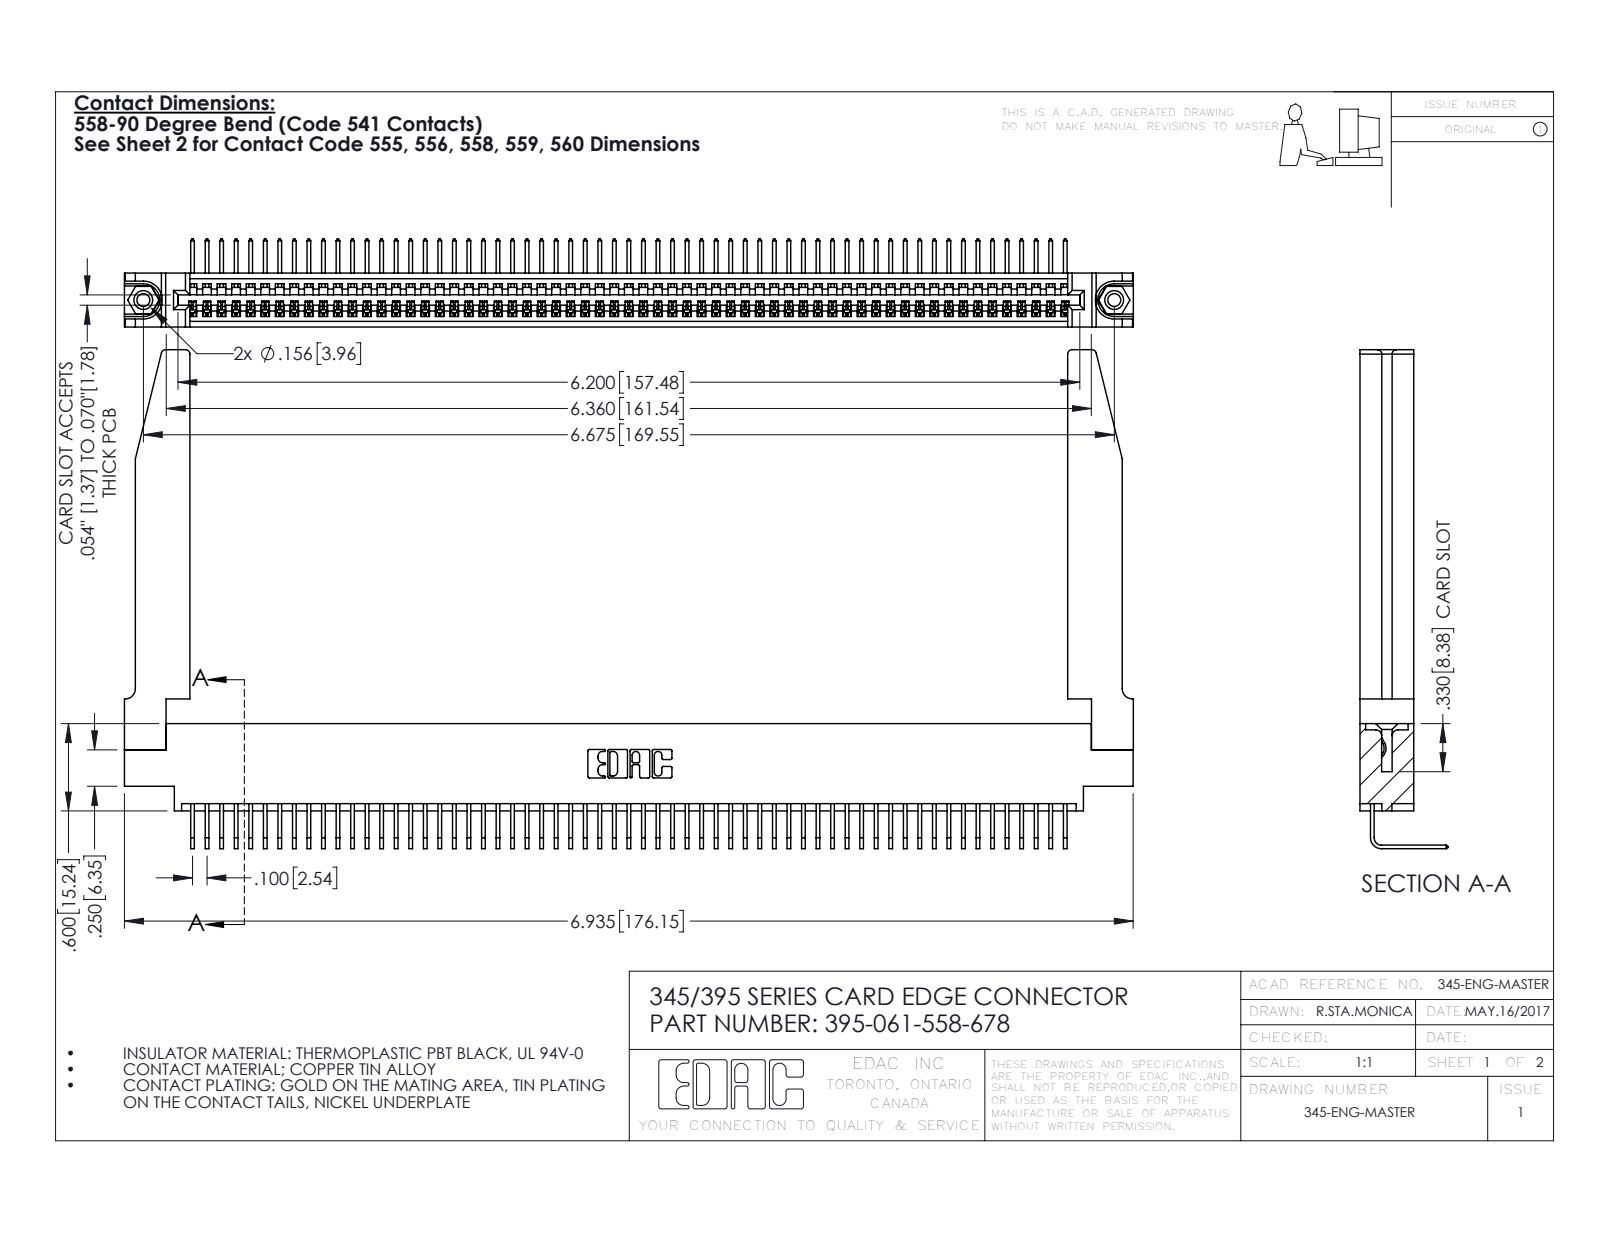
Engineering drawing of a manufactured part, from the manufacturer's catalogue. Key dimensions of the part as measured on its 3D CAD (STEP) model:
Part name (STEP PRODUCT): 345 Part_0.170 Offset - 0.156 Dia-TH; 395-061-558-678; 345-220-078_345-220-078; 345-250-001_345-250-001-102 (+1 more)
STEP written by: SolidWorks 2016 (CONFIG_CONTROL_DESIGN)
Units: inches
Bodies: 66 solids, 4024 faces (2788 planar, 1184 cylindrical, 52 other)
Overall size (bounding box): 6.936 × 3.429 × 0.605
Volume: 1.51 in³ · Surface area: 48.03 in²
Round holes (diameter × count): ⌀0.089 ×2, ⌀0.125 ×2, ⌀0.156 ×2, ⌀0.064 ×1
Round bosses / shafts (diameter × count): ⌀0.155 ×2
Partial cylindrical surfaces — rounded edges, fillets, slot ends (radius × count): R0.006 ×122, R0.01 ×22, R0.03 ×8, R0.007 ×6, R0.031 ×6, R0.026 ×3, R0.031 ×2, R0.04 ×2
Main face-to-face distances: 0.37, 0.072, 0.298, 0.098, 0.272, 0.025, 0.2, 0.225, 0.148, 0.15
Hole centre spacings: 0.27, 6.439, 6.675
